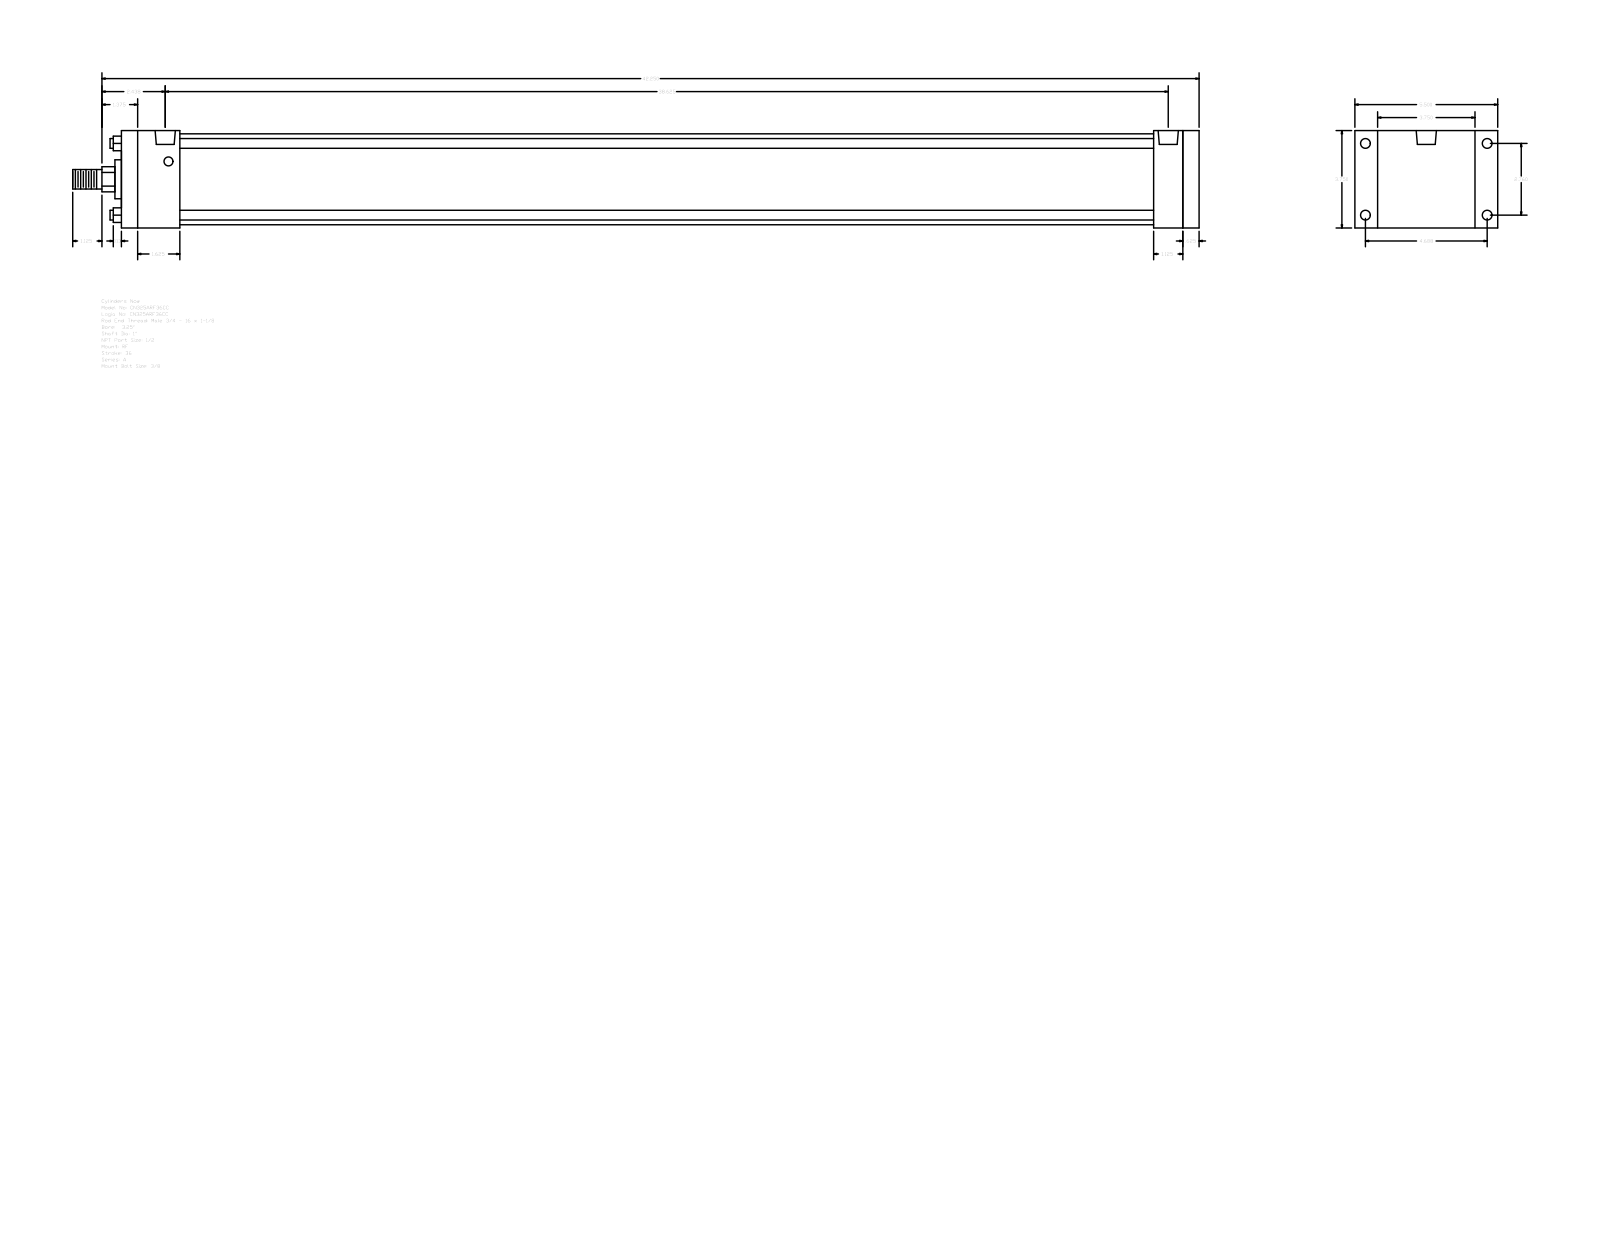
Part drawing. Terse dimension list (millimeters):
name: A_RF__0325_1
written by: GSSL Pune (CONFIG_CONTROL_DESIGN)
unit: mm
bodies: 0 solids, 92 faces (64 planar, 28 cylindrical, 0 other)
size: 1101.72 × 139.7 × 95.25
holes: 4× ⌀8.73, 4× ⌀9.53, 2× ⌀19.77
bosses: 4× ⌀9.53, 1× ⌀88.9, 1× ⌀38.1, 1× ⌀25.4, 1× ⌀19.05
rounds: 1× R12.29
face distances: 95.24, 1054.1, 1038.23, 15.87, 22.23, 117.47, 1009.65, 28.58, 44.45, 57.15
hole spacings: 3.18, 70.1, 119.06, 138.16, 974.72, 977.9, 981.08
